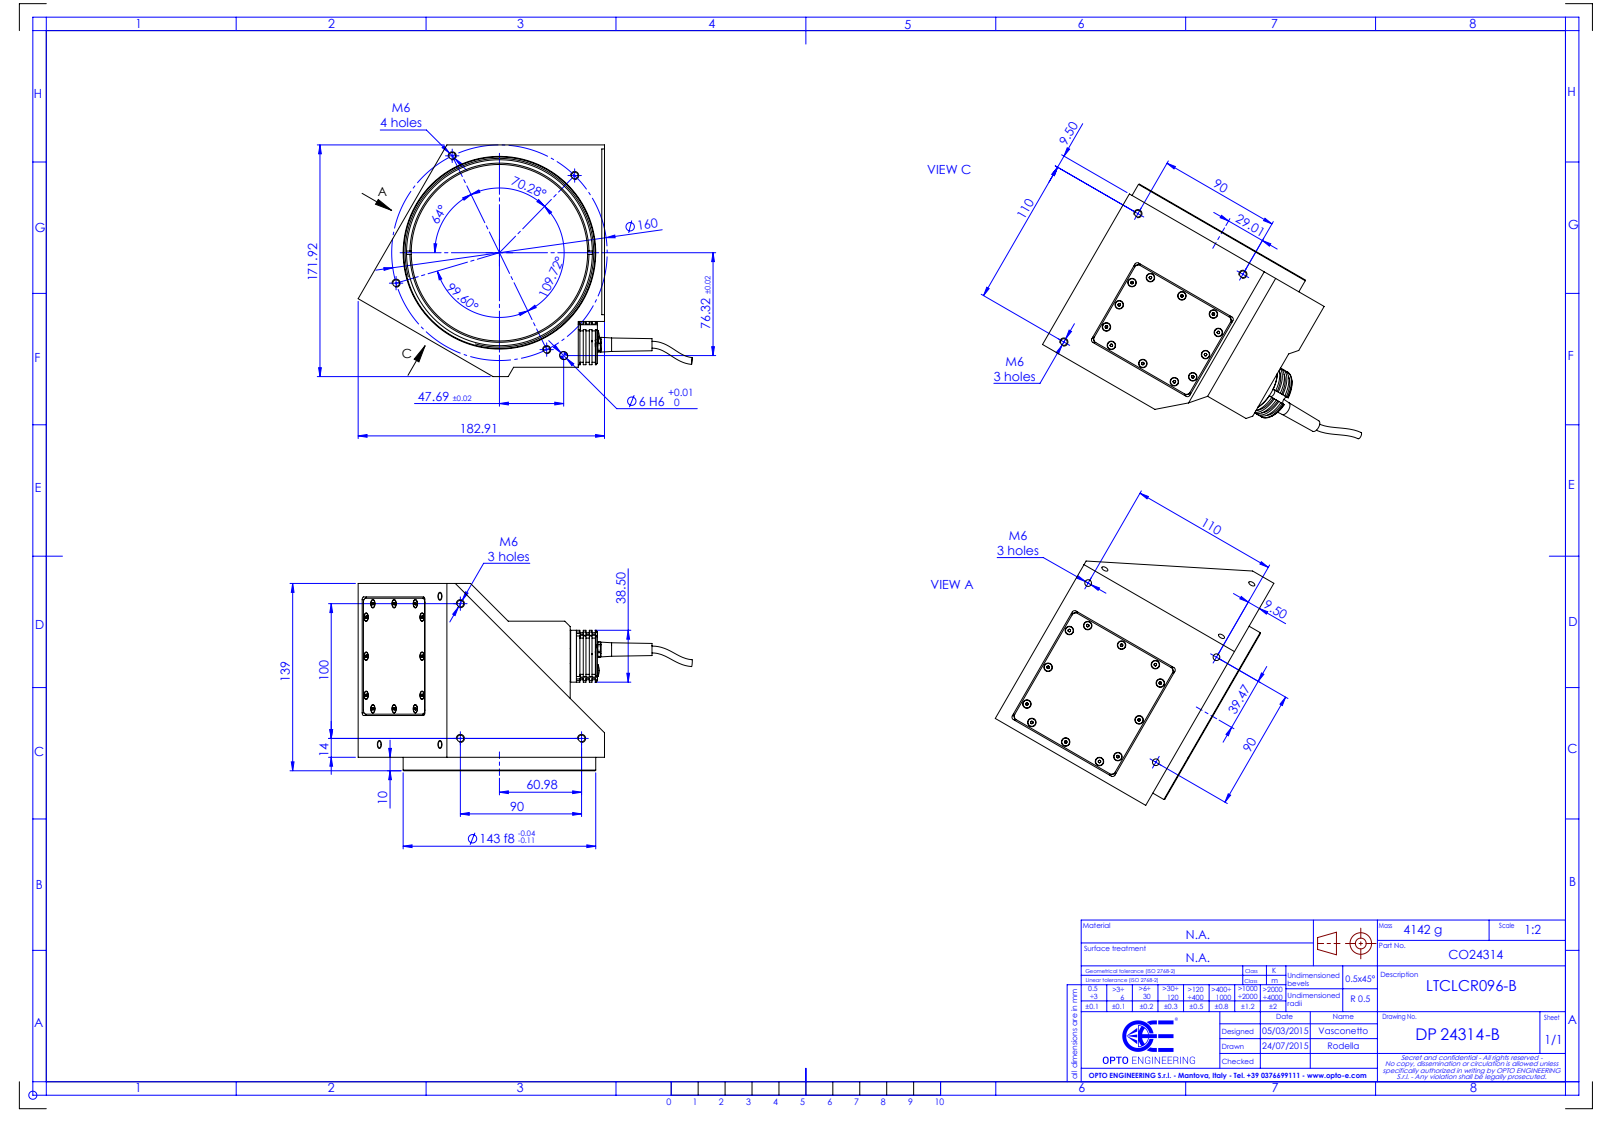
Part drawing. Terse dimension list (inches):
name: DP24314-B_LTCLCR096-B
written by: SolidWorks 2021 (CONFIG_CONTROL_DESIGN)
unit: in
bodies: 0 solids, 564 faces (240 planar, 160 cylindrical, 164 other)
size: 9.768 × 6.769 × 5.472
holes: 13× ⌀0.197, 3× ⌀0.157, 1× ⌀0.236, 1× ⌀5.157, 1× ⌀5.433
bosses: 30× ⌀0.226, 3× ⌀0.217, 1× ⌀5.63, 1× ⌀1.516, 1× ⌀1.374, 1× ⌀0.354
rounds: 8× R0.079, 8× R0.118, 3× R0.114, 2× R0.157
face distances: 0.02, 5.079, 6.496, 0.315, 1.535, 4.961, 0.394, 0.236, 4.291, 1.003
hole spacings: 3.15, 3.543, 1.04, 4.331, 5.596, 0.526, 1.04, 3.543
